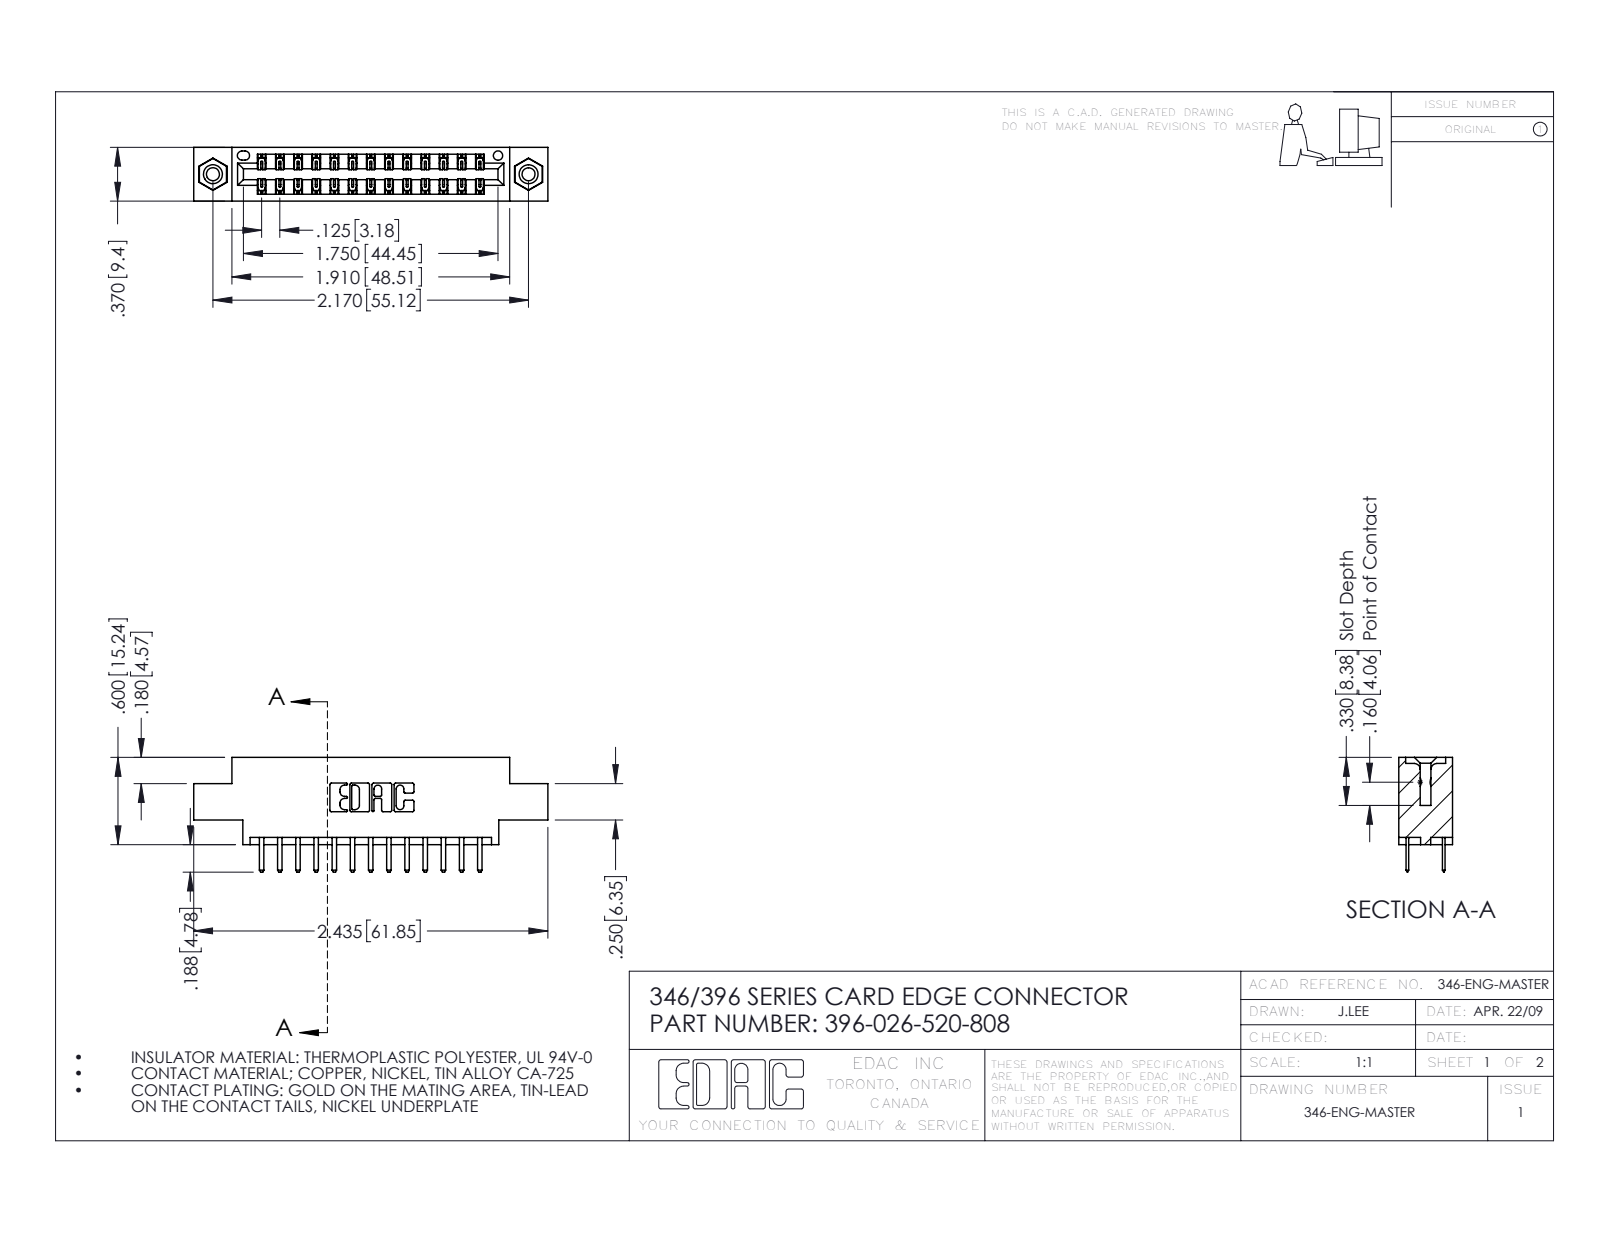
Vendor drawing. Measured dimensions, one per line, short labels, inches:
name: 396-026-520-808; 345-250-001_345-250-003-102; 346 Part_0.170 Offset - 0.156 Dia-TI; 345-292-001_345-293-120
written by: SolidWorks 2016 (CONFIG_CONTROL_DESIGN)
unit: in
bodies: 29 solids, 1642 faces (1074 planar, 552 cylindrical, 16 other)
size: 2.435 × 0.788 × 0.37
volume: 0.344 in³; area: 11.56 in²
holes: 2× ⌀0.089, 2× ⌀0.125, 2× ⌀0.156, 1× ⌀0.064
bosses: 2× ⌀0.155
rounds: 39× R0.006, 30× R0.01, 22× R0.01, 6× R0.007, 6× R0.031, 3× R0.026, 2× R0.014, 2× R0.022
face distances: 0.25, 0.048, 0.322, 0.37, 0.222, 0.148, 0.275, 0.072, 0.298, 0.025
hole spacings: 0.246, 1.964, 2.17
